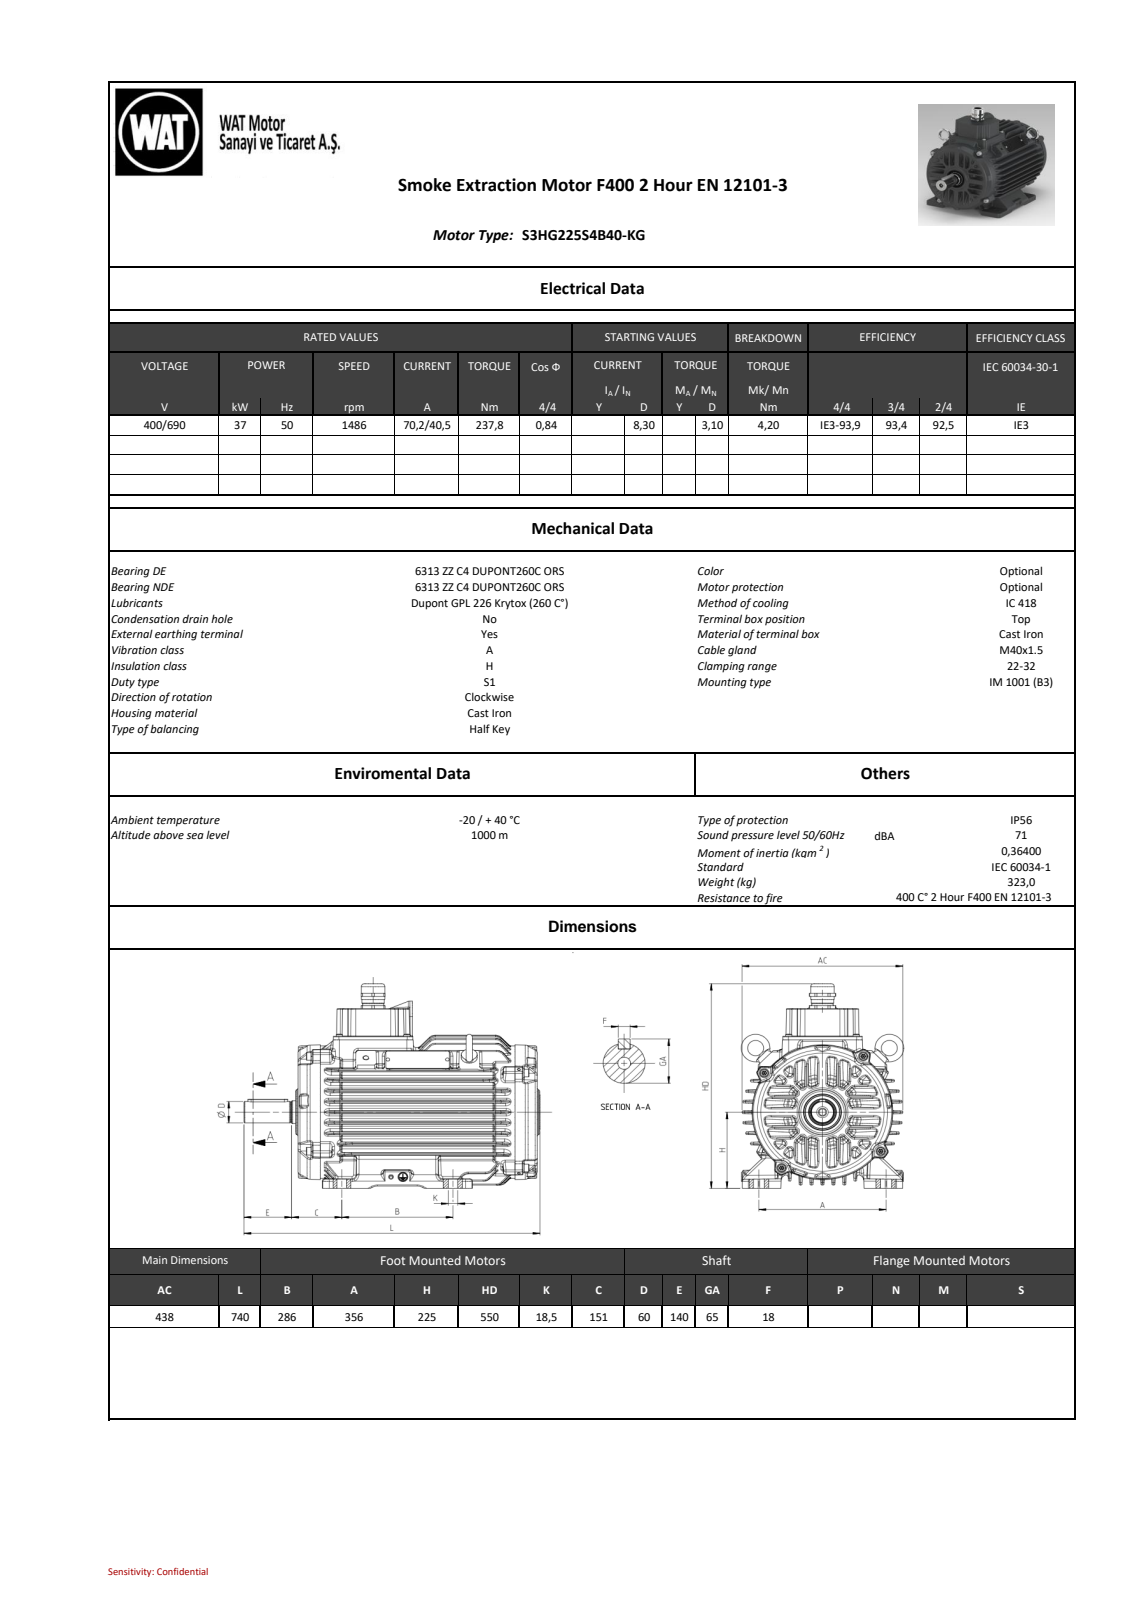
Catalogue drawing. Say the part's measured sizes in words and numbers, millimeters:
The part is named "260381480CFDz4fi". Its 3-D file was written by "SIEMENS PLM Software NX 11.0 (AUTOMOTIVE_DESIGN)". It is 0 solids with 7175 faces: 926 planar, 1630 cylindrical and 4619 other. Overall it measures 740 by 550 by 443 millimeters. Round holes: 10 of diameter 14, 5 of diameter 6.8, 1 of diameter 2.5, 1 of diameter 21, 1 of diameter 32, 1 of diameter 82, 1 of diameter 88.33, 1 of diameter 100. Round bosses or shafts: 8 of diameter 30, 4 of diameter 24, 4 of diameter 23.67, 4 of diameter 12, 2 of diameter 35, 1 of diameter 372, 1 of diameter 76.67, 1 of diameter 65. Partial cylindrical surfaces (rounded edges, fillets, slot ends): 333 of radius 4, 233 of radius 2, 146 of radius 5, 139 of radius 3, 82 of radius 6, 47 of radius 0.6, 19 of radius 10, 16 of radius 0.5. The main face-to-face distances are 17.41, 159.69, 17.32, 194.42, 34.89, 142.21, 17.48, 88.37, 52.44, 35.03. The hole center spacings are 198, 280.01, 68.76, 227.14, 324.38, 389.98, 396, 127.5.
